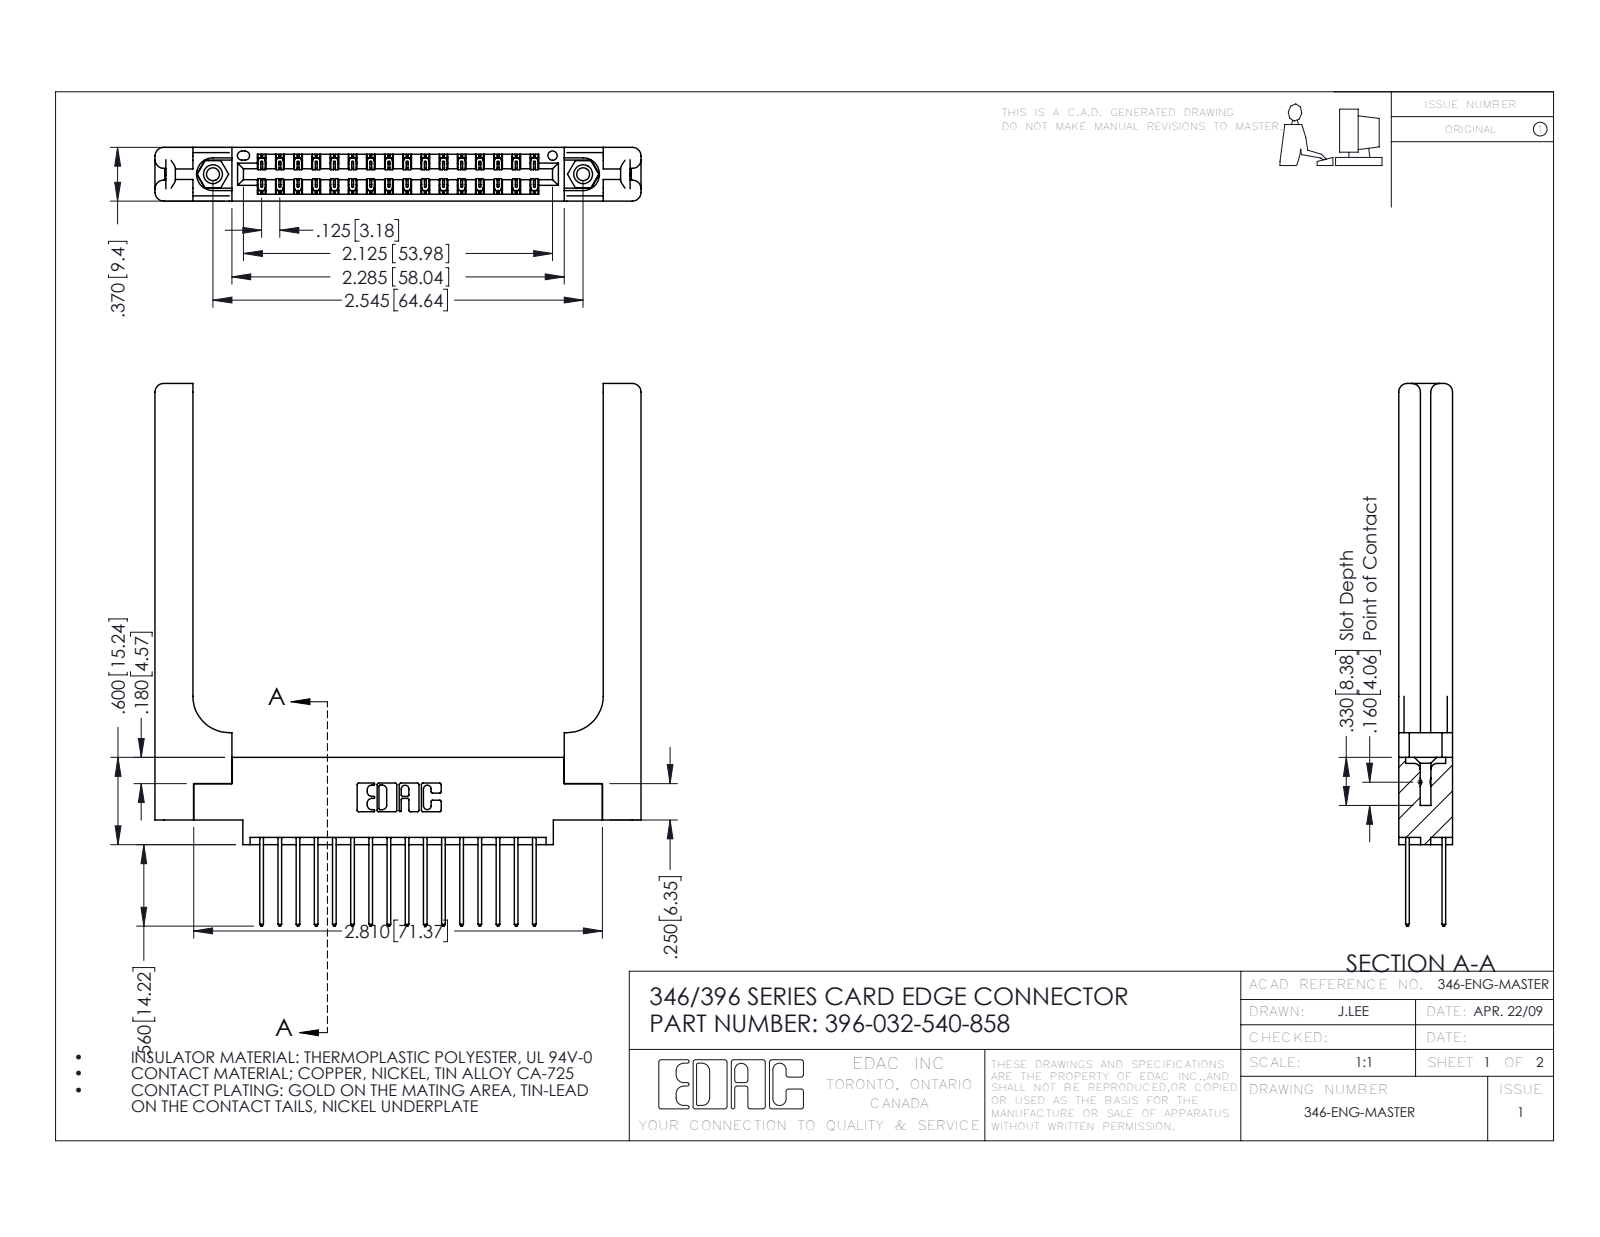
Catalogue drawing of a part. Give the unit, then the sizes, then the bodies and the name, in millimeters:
Units: millimetres
Overall size (bounding box): 94.7 × 84.9 × 9.4
Round holes (diameter × count): ⌀2.3 ×2, ⌀3.2 ×2, ⌀4 ×2, ⌀1.6 ×1
Round bosses / shafts (diameter × count): ⌀3.9 ×2
Partial cylindrical surfaces — rounded edges, fillets, slot ends (radius × count): R0.2 ×48, R0.3 ×32, R0.3 ×22, R1.5 ×16, R0.2 ×6, R0.8 ×6, R0.7 ×3, R0.4 ×2
Main face-to-face distances: 9.4, 1.8, 1.2, 8.2, 3.8, 3.8, 6.4, 0.6, 7.6, 2
Hole centre spacings: 6.2, 59.4, 64.6
Volume: 15 500 mm³ · Surface area: 16 370 mm²
Bodies: 37 solids, 2046 faces (1348 planar, 638 cylindrical, 60 other)
Part name (STEP PRODUCT): 346-220-058_345-220-058; 396-032-540-858; 346 Part_0.170 Offset - 0.156 Dia-TH; 345-250-001_345-250-001-102 (+1 more)
STEP written by: SolidWorks 2016 (CONFIG_CONTROL_DESIGN)
